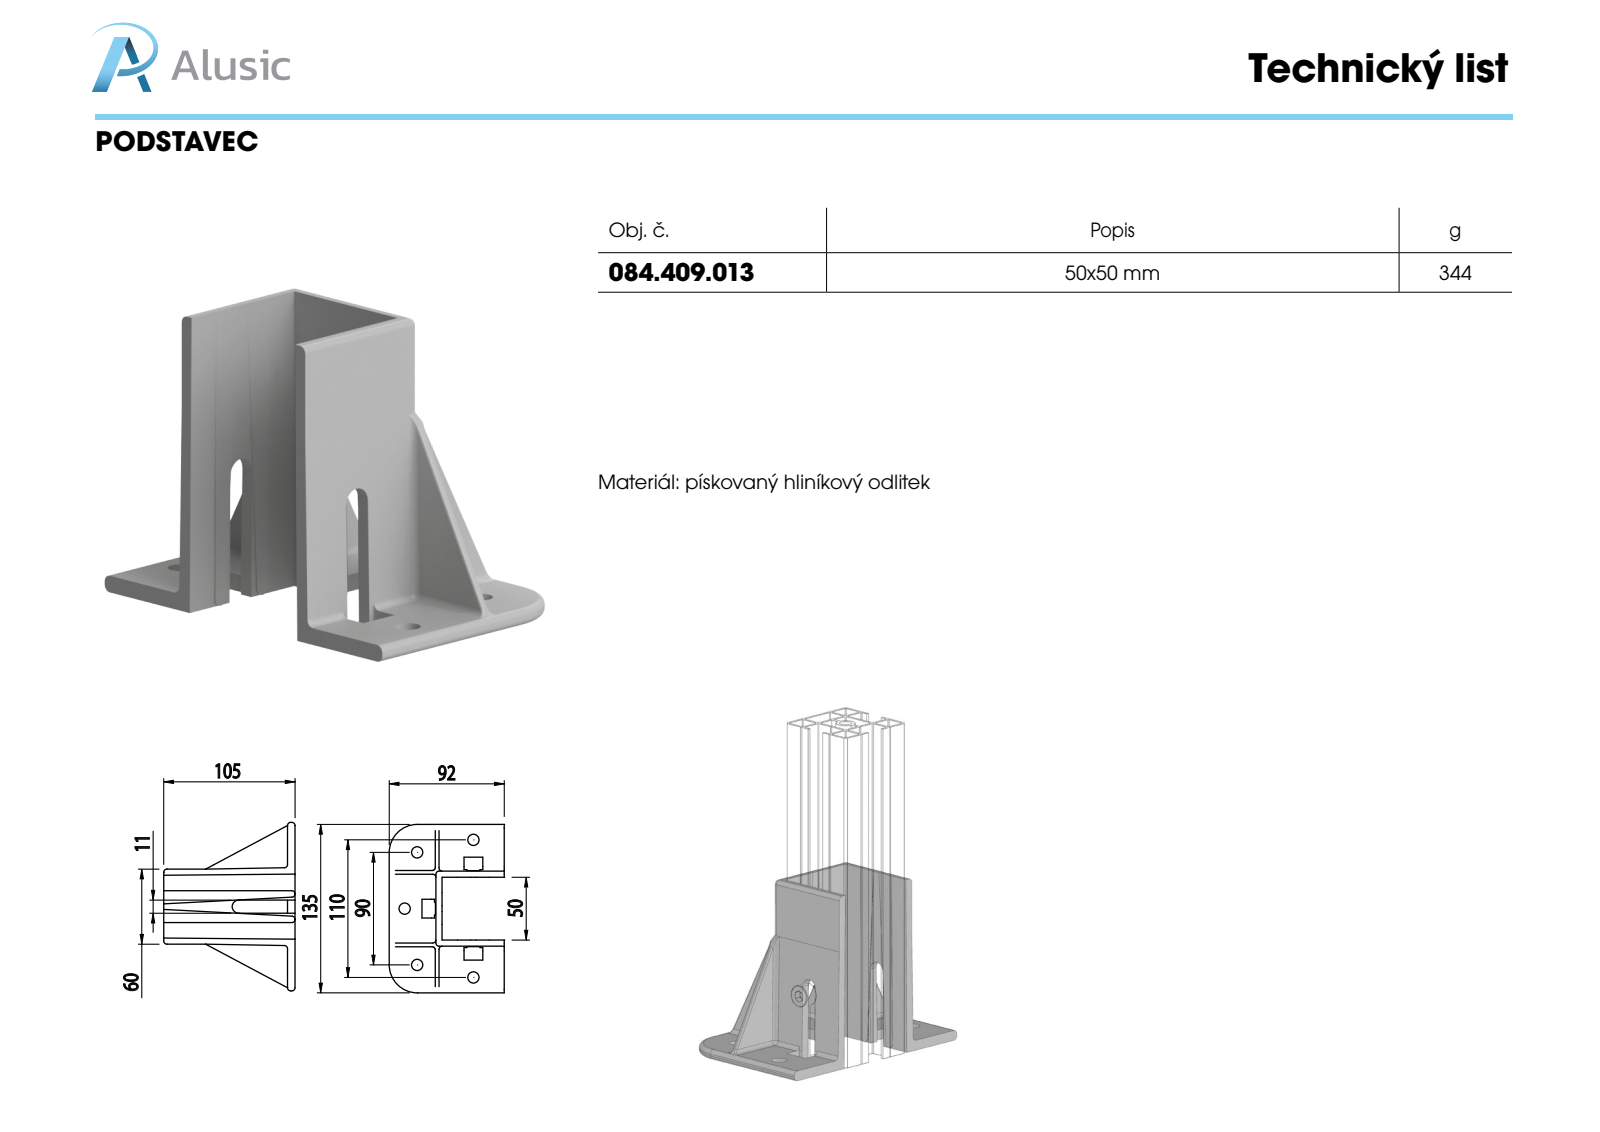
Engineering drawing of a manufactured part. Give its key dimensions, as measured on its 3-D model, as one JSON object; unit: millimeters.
{"part_name": "084.409.013", "step_written_by": "SolidWorks 2012 (CONFIG_CONTROL_DESIGN)", "units": "millimeters", "bodies": {"solids": 1, "faces": 189, "planar": 84, "cylindrical": 70, "other": 35}, "overall_size": [134.7, 105, 92], "volume_mm3": 128984, "surface_area_mm2": 62186, "round_holes": [[9, 5]], "partial_cylinders_radius": [[2.5, 33], [1, 9], [5.25, 2], [22.5, 2]], "face_to_face_distances": [6, 3, 2.5, 0.5, 57.5, 60.5, 58, 60, 52.15, 54.65], "hole_center_spacings": [46.1, 77.78, 109.66, 90, 110]}
